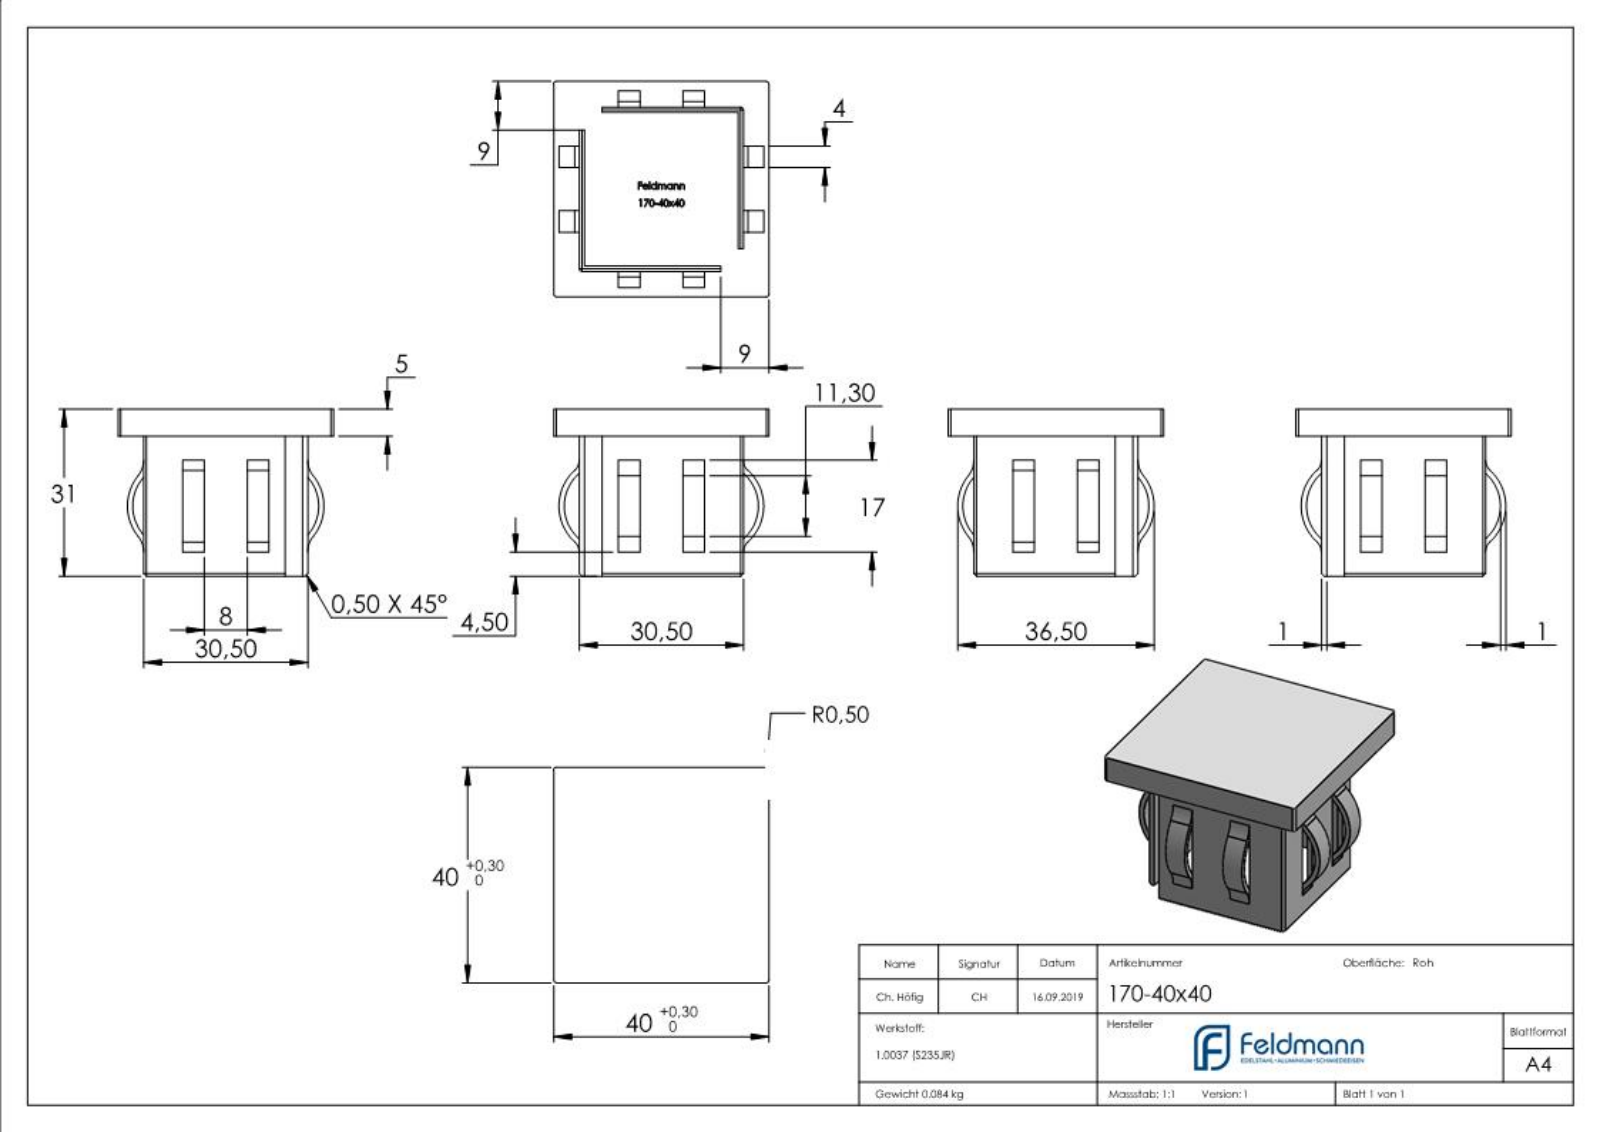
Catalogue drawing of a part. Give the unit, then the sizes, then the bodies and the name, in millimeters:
Units: millimetres
Overall size (bounding box): 40 × 40 × 31
Partial cylindrical surfaces — rounded edges, fillets, slot ends (radius × count): R2 ×8, R3.5 ×8, R0.5 ×6, R12.06 ×4, R13.06 ×4
Main face-to-face distances: 31, 1.5, 5, 32.5, 29.5, 3.75, 5.25, 34.75, 36.25, 15.5
Volume: 11 962 mm³ · Surface area: 10 169 mm²
Bodies: 1 solid, 320 faces (189 planar, 54 cylindrical, 77 other)
Part name (STEP PRODUCT): 170-40X40
STEP written by: SolidWorks 2018 (CONFIG_CONTROL_DESIGN)
